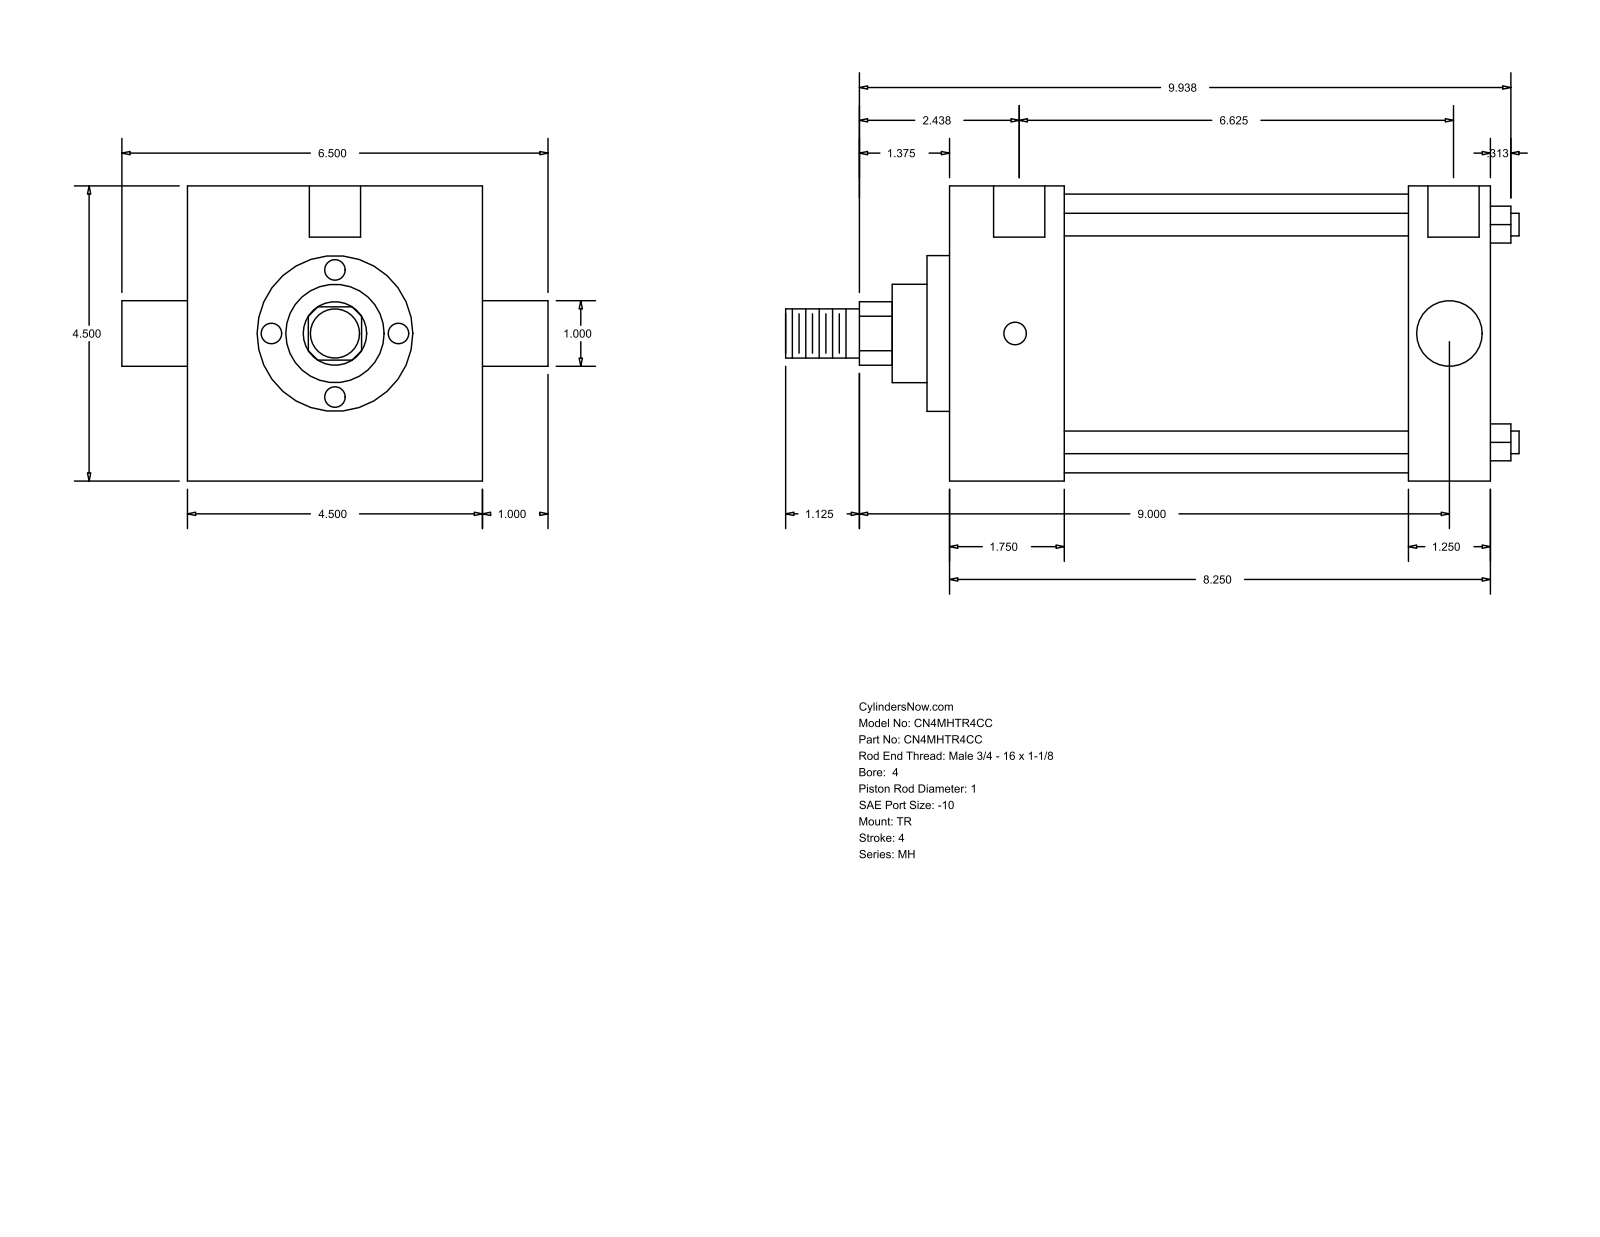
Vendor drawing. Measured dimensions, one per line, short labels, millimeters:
name: MH_TR__0400_1
written by: GSSL Pune (CONFIG_CONTROL_DESIGN)
unit: mm
bodies: 0 solids, 86 faces (61 planar, 25 cylindrical, 0 other)
size: 284.16 × 165.1 × 114.3
holes: 3× ⌀8.73, 2× ⌀19.84
bosses: 4× ⌀8.76, 2× ⌀25.4, 1× ⌀107.95, 1× ⌀60.33, 1× ⌀38.1, 1× ⌀19.05
rounds: 1× R12.29
face distances: 114.3, 209.55, 44.46, 165.09, 177.8, 133.34, 31.75, 8.73, 53.19, 186.53
hole spacings: 1.58, 1.59, 168.28, 169.86, 169.87, 171.45
